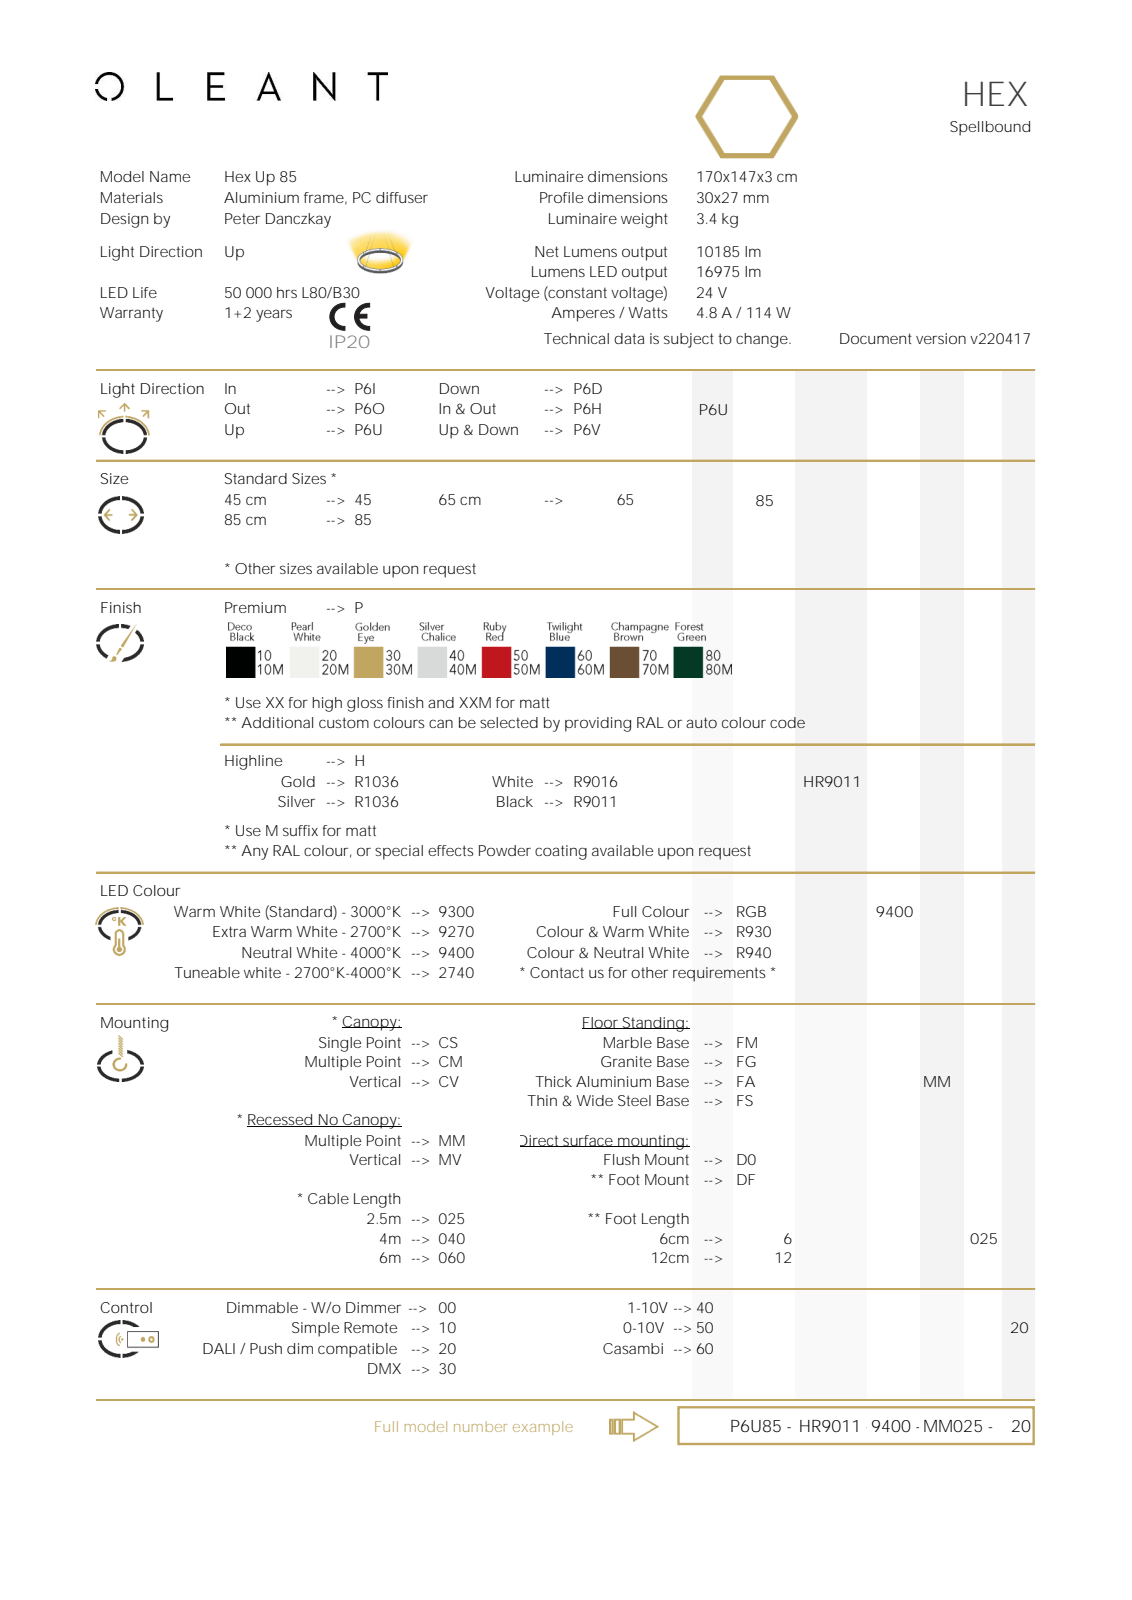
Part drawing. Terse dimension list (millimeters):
name: polygon_even; frame; plexi; cable (+1 more)
written by: Autodesk Inventor 2020 (AUTOMOTIVE_DESIGN)
unit: mm
bodies: 8 solids, 154 faces (109 planar, 39 cylindrical, 6 other)
size: 1700 × 1472.24 × 1049.5
volume: 3 829 000 mm³; area: 1 309 000 mm²
holes: 3× ⌀3
bosses: 3× ⌀11, 3× ⌀9, 3× ⌀4, 3× ⌀1.2
rounds: 24× R0.75
face distances: 2, 1442.21, 24.5, 22.5, 1442.24, 1444.21, 28.01, 28, 27.99, 1440.21
hole spacings: 1442.24
